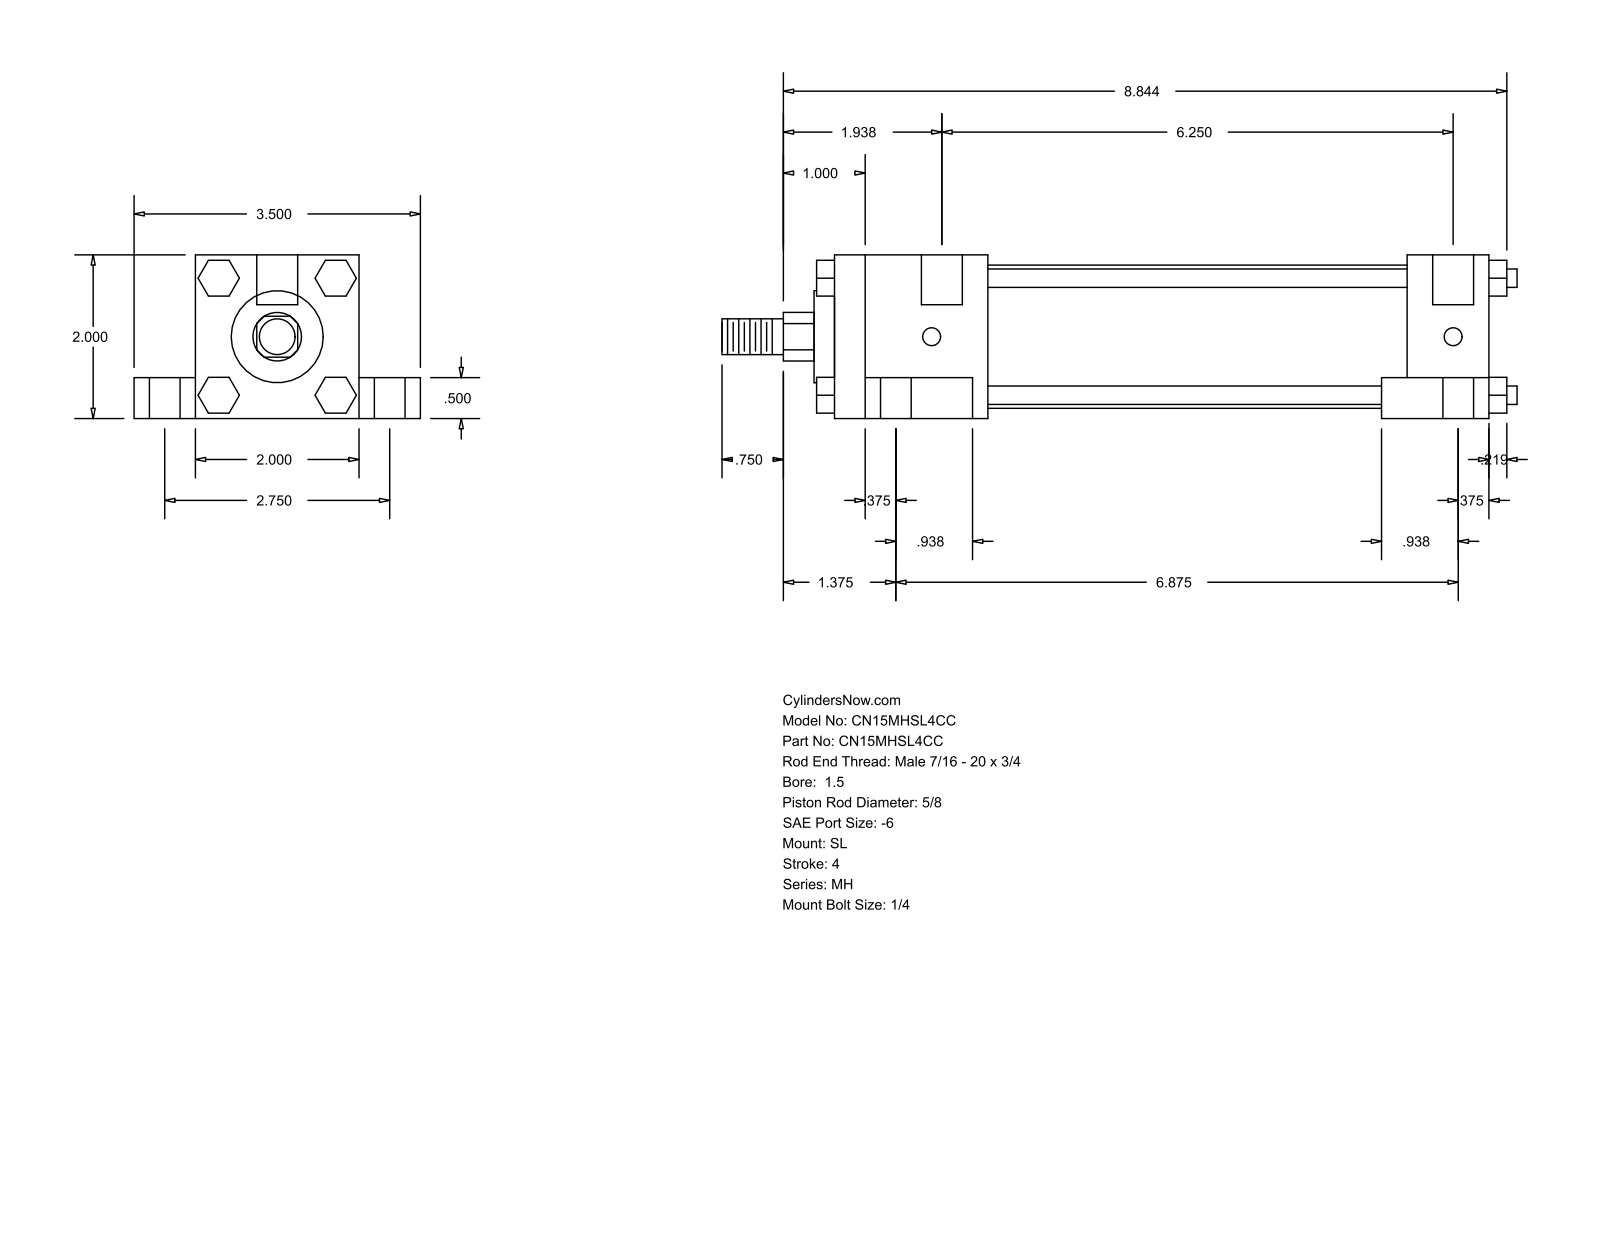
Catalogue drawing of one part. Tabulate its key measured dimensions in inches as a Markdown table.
| quantity | value |
| --- | --- |
| part name | MH_SL__0150_0.625 |
| STEP written by | GSSL Pune (CONFIG_CONTROL_DESIGN) |
| units | inches |
| bodies | 0 solids, 148 faces (112 planar, 36 cylindrical, 0 other) |
| overall size | 9.719 × 3.5 × 2 |
| round holes (diameter × count) | 0.219 × 4, 0.375 × 4, 0.625 × 4, 0.5 × 2 |
| round bosses / shafts (diameter × count) | 0.225 × 4, 1.75 × 1, 1.125 × 1, 0.625 × 1, 0.437 × 1 |
| partial cylindrical surfaces (radius × count) | 0.297 × 1 |
| main face-to-face distances | 2, 1.5, 0.75, 0.5, 2.75, 8, 0.375, 7, 1, 1.875 |
| hole center spacings | 1.376, 1.443, 1.485, 2.75, 6.375, 6.461, 6.583, 6.875 |
